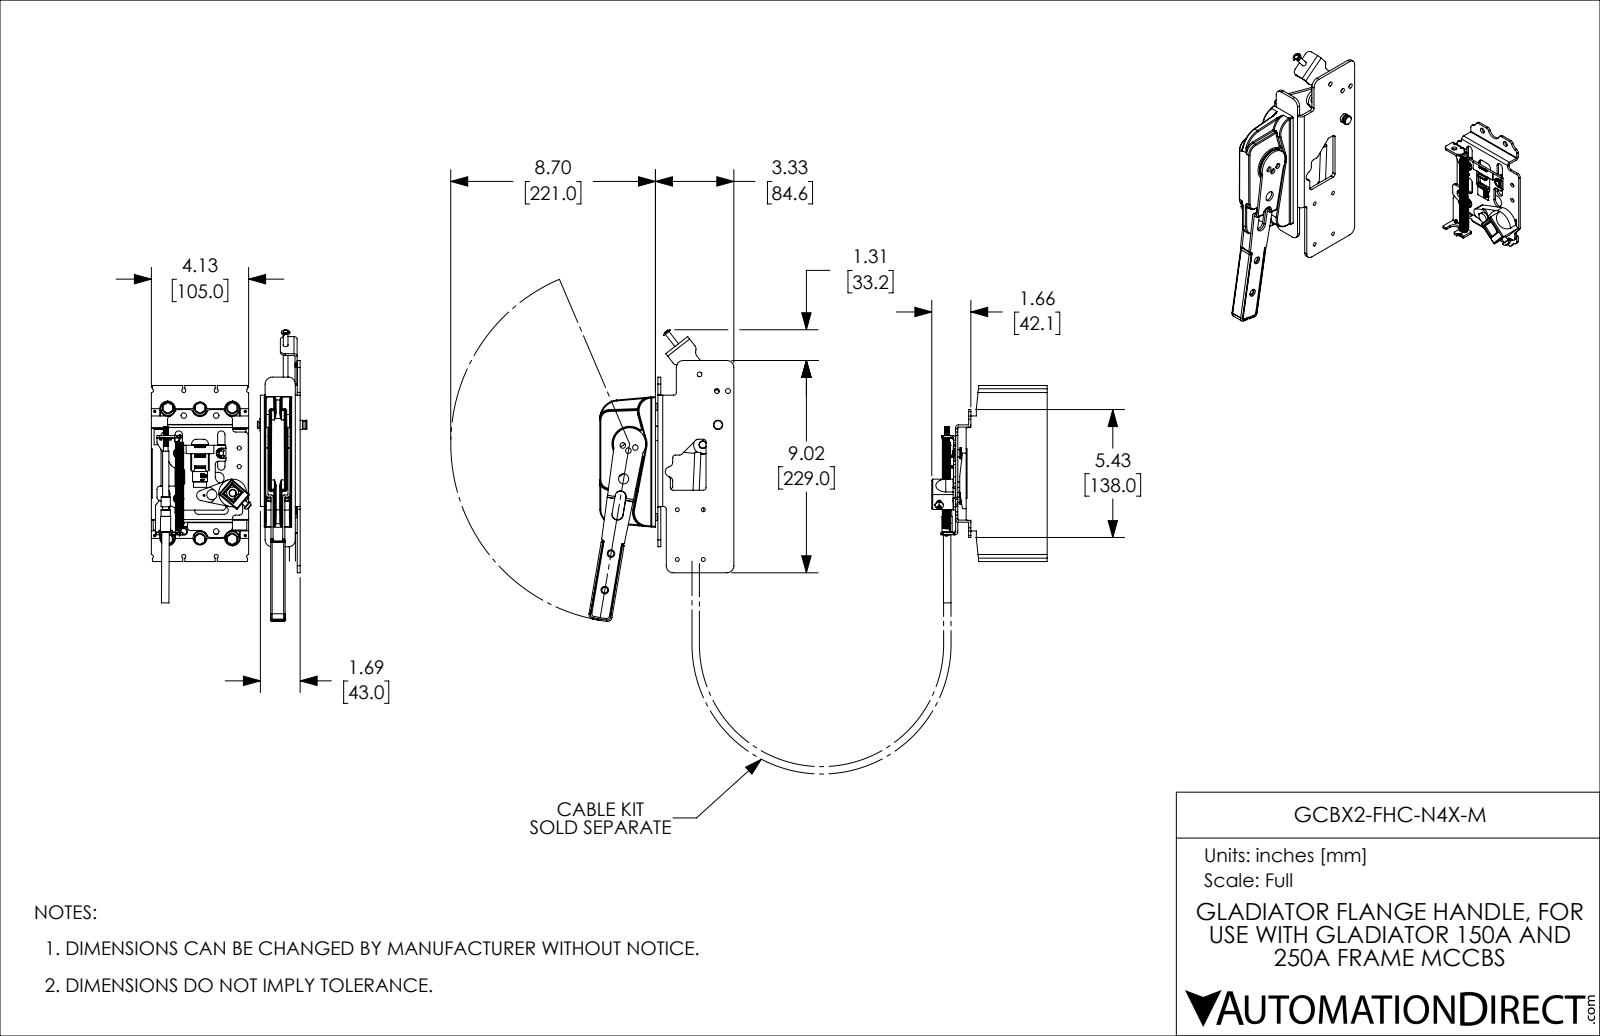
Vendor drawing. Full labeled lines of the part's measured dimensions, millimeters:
Part name (STEP PRODUCT): GCBX2-FHC-N4X-M_1; GCBX2-FHC-N4X-M_2; GCB250S-3FF250LL; GCBX2-FHC-N4X-M (+1 more)
STEP written by: SolidWorks 2021 (CONFIG_CONTROL_DESIGN)
Units: millimetres
Bodies: 40 solids, 4794 faces (2462 planar, 1758 cylindrical, 574 other)
Overall size (bounding box): 494.7 × 314.8 × 167.9
Volume: 1 708 000 mm³ · Surface area: 399 100 mm²
Round holes (diameter × count): ⌀4 ×25, ⌀1.7 ×24, ⌀2.5 ×10, ⌀6 ×6, ⌀6.2 ×6, ⌀9 ×6, ⌀15 ×6, ⌀17.5 ×6, ⌀4.2 ×4, ⌀4.4 ×4, ⌀5.1 ×4, ⌀5.2 ×4
Round bosses / shafts (diameter × count): ⌀5 ×8, ⌀18 ×6, ⌀10 ×5, ⌀4 ×5, ⌀8 ×4, ⌀12 ×3, ⌀11 ×3, ⌀7.8 ×3
Partial cylindrical surfaces — rounded edges, fillets, slot ends (radius × count): R0.3 ×210, R1 ×150, R0.5 ×65, R1.5 ×48, R2 ×42, R3 ×35, R3.5 ×34, R0.2 ×30
Main face-to-face distances: 3.2, 2.3, 105, 52.4, 55.6, 157.4, 160.6, 34.7, 5.6, 18.3
Hole centre spacings: 35, 133.1, 18.9, 26.6, 160, 151.9, 14.2, 27.1
